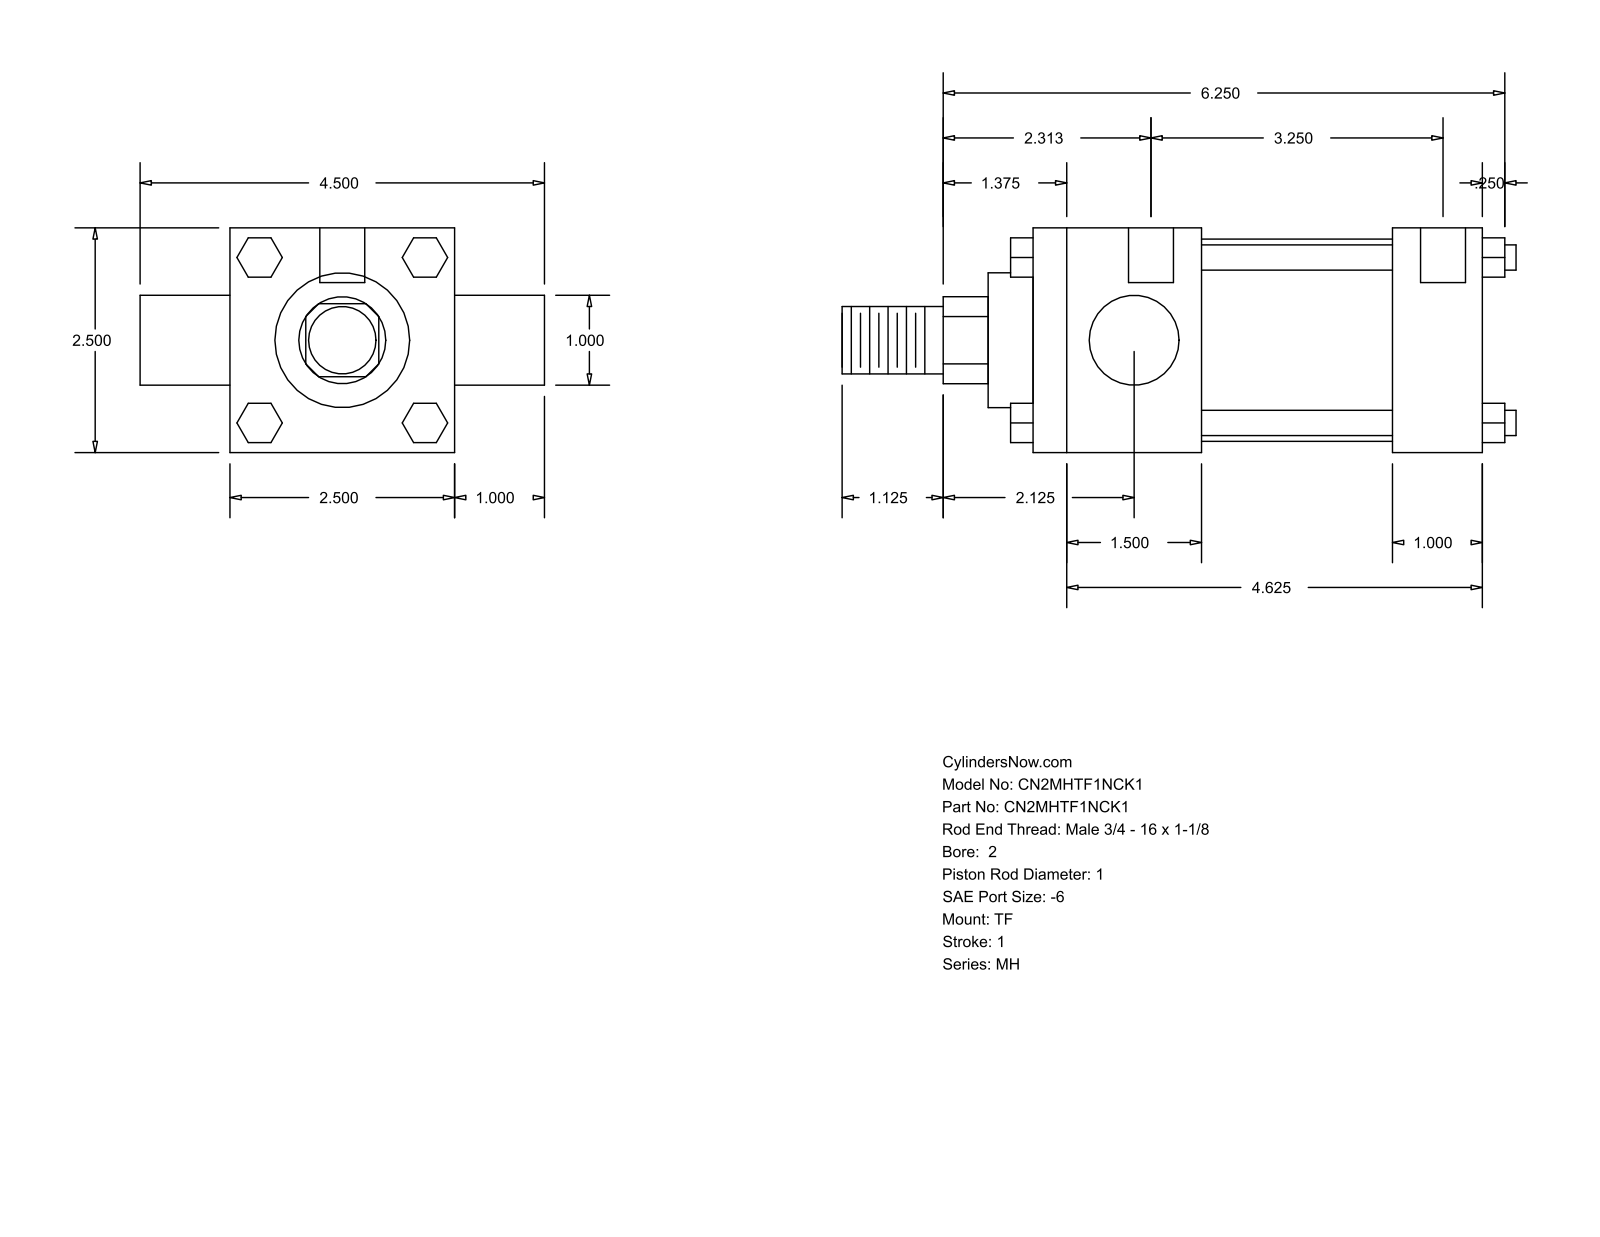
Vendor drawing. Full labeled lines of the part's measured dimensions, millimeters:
Part name (STEP PRODUCT): MH_TF__0200_1
STEP written by: GSSL Pune (CONFIG_CONTROL_DESIGN)
Units: millimetres
Bodies: 0 solids, 120 faces (92 planar, 28 cylindrical, 0 other)
Overall size (bounding box): 190.5 × 114.3 × 63.5
Round holes (diameter × count): ⌀5.56 ×3, ⌀12.7 ×2
Round bosses / shafts (diameter × count): ⌀7.14 ×4, ⌀25.4 ×2, ⌀57.15 ×1, ⌀38.1 ×1, ⌀19.05 ×1
Partial cylindrical surfaces — rounded edges, fillets, slot ends (radius × count): R12.29 ×1
Main face-to-face distances: 63.5, 127, 25.4, 53.97, 101.6, 47.63, 79.37, 88.9, 114.3, 139.7
Hole centre spacings: 3.17, 4.76, 82.55, 85.72, 87.31, 90.48
